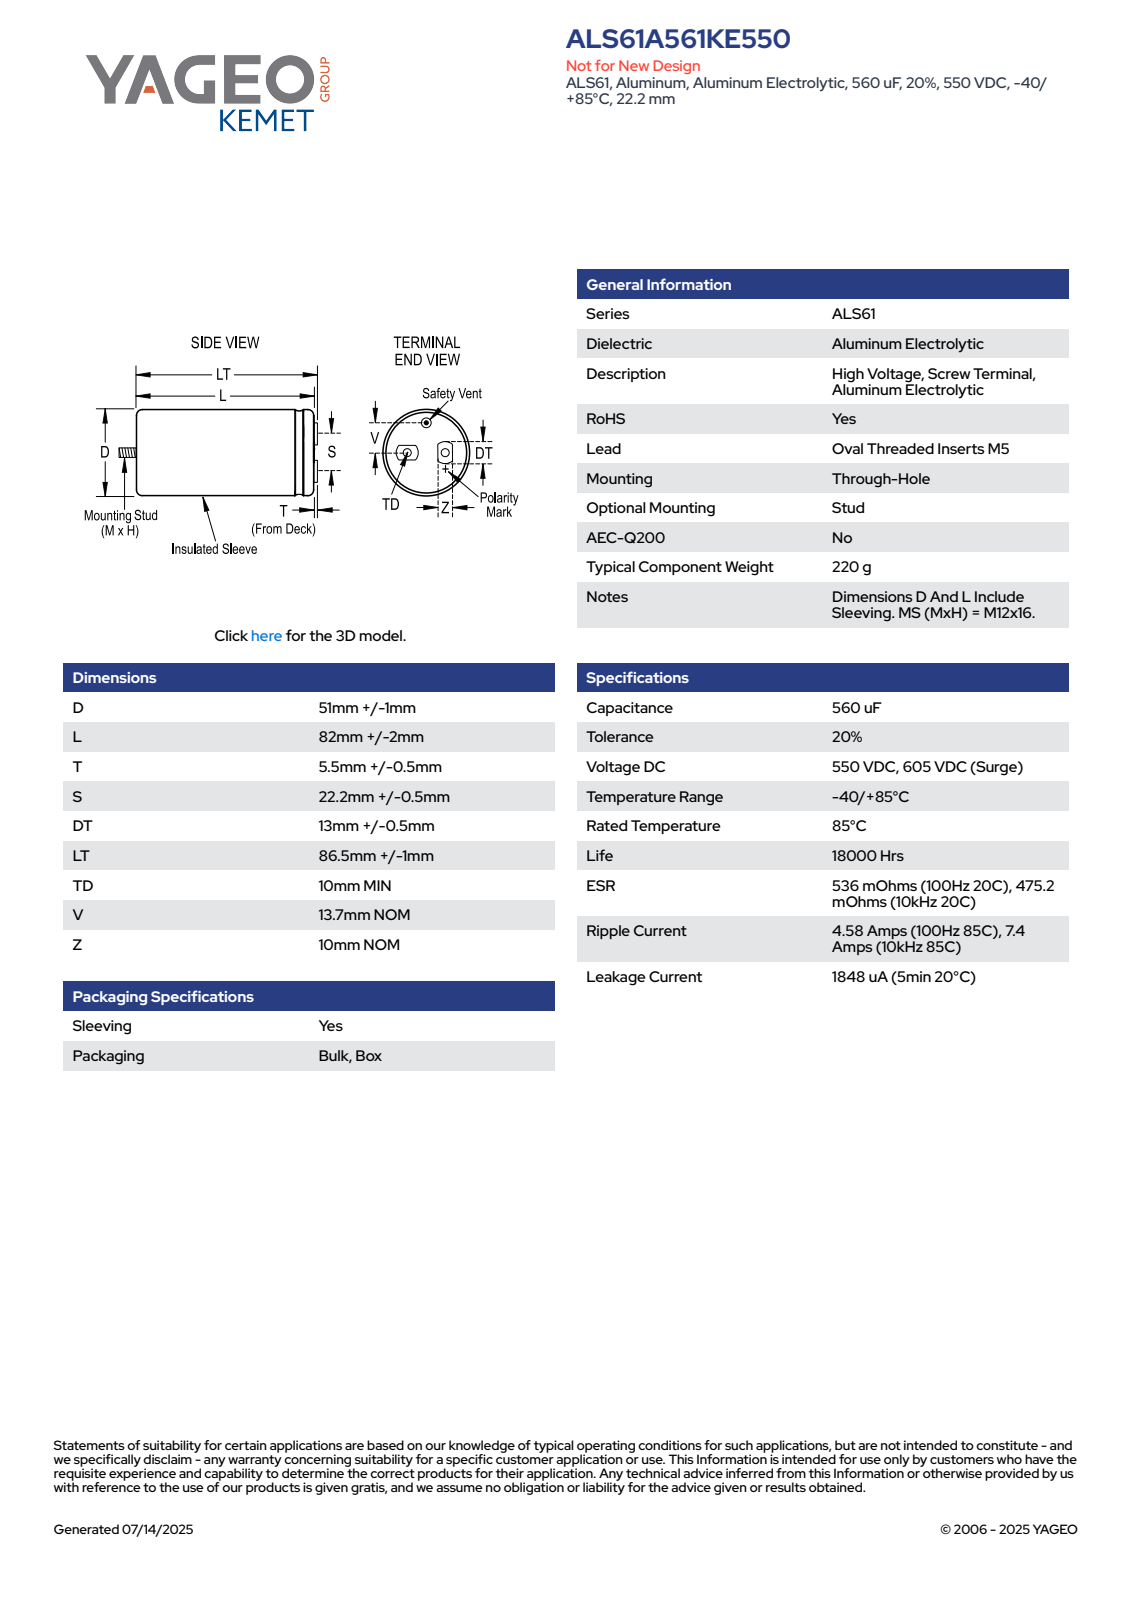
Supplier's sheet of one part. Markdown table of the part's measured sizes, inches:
| quantity | value |
| --- | --- |
| part name | CARC_KALSOS_51X82_D52.00L84.00T6.00S22.2DT13.500TD10.000LT87.500V13.700 |
| STEP written by | SolidWorks 2014 (AUTOMOTIVE_DESIGN) |
| units | inches |
| bodies | 1 solid, 98 faces (35 planar, 24 cylindrical, 39 other) |
| overall size | 4.075 × 2.047 × 2.047 |
| volume | 10.85 in³ |
| surface area | 30.17 in² |
| round holes (diameter × count) | 0.197 × 2, 0.079 × 1, 1.89 × 1 |
| round bosses / shafts (diameter × count) | 2.047 × 1, 0.472 × 1, 0.118 × 1 |
| partial cylindrical surfaces (radius × count) | 0.315 × 4, 1.023 × 1 |
| main face-to-face distances | 3.268, 3.445, 0.177, 0.394, 0.63, 3.898, 4.075, 3.681, 3.051, 0.217 |
| hole center spacings | 0.437, 0.694, 0.539, 0.874 |
